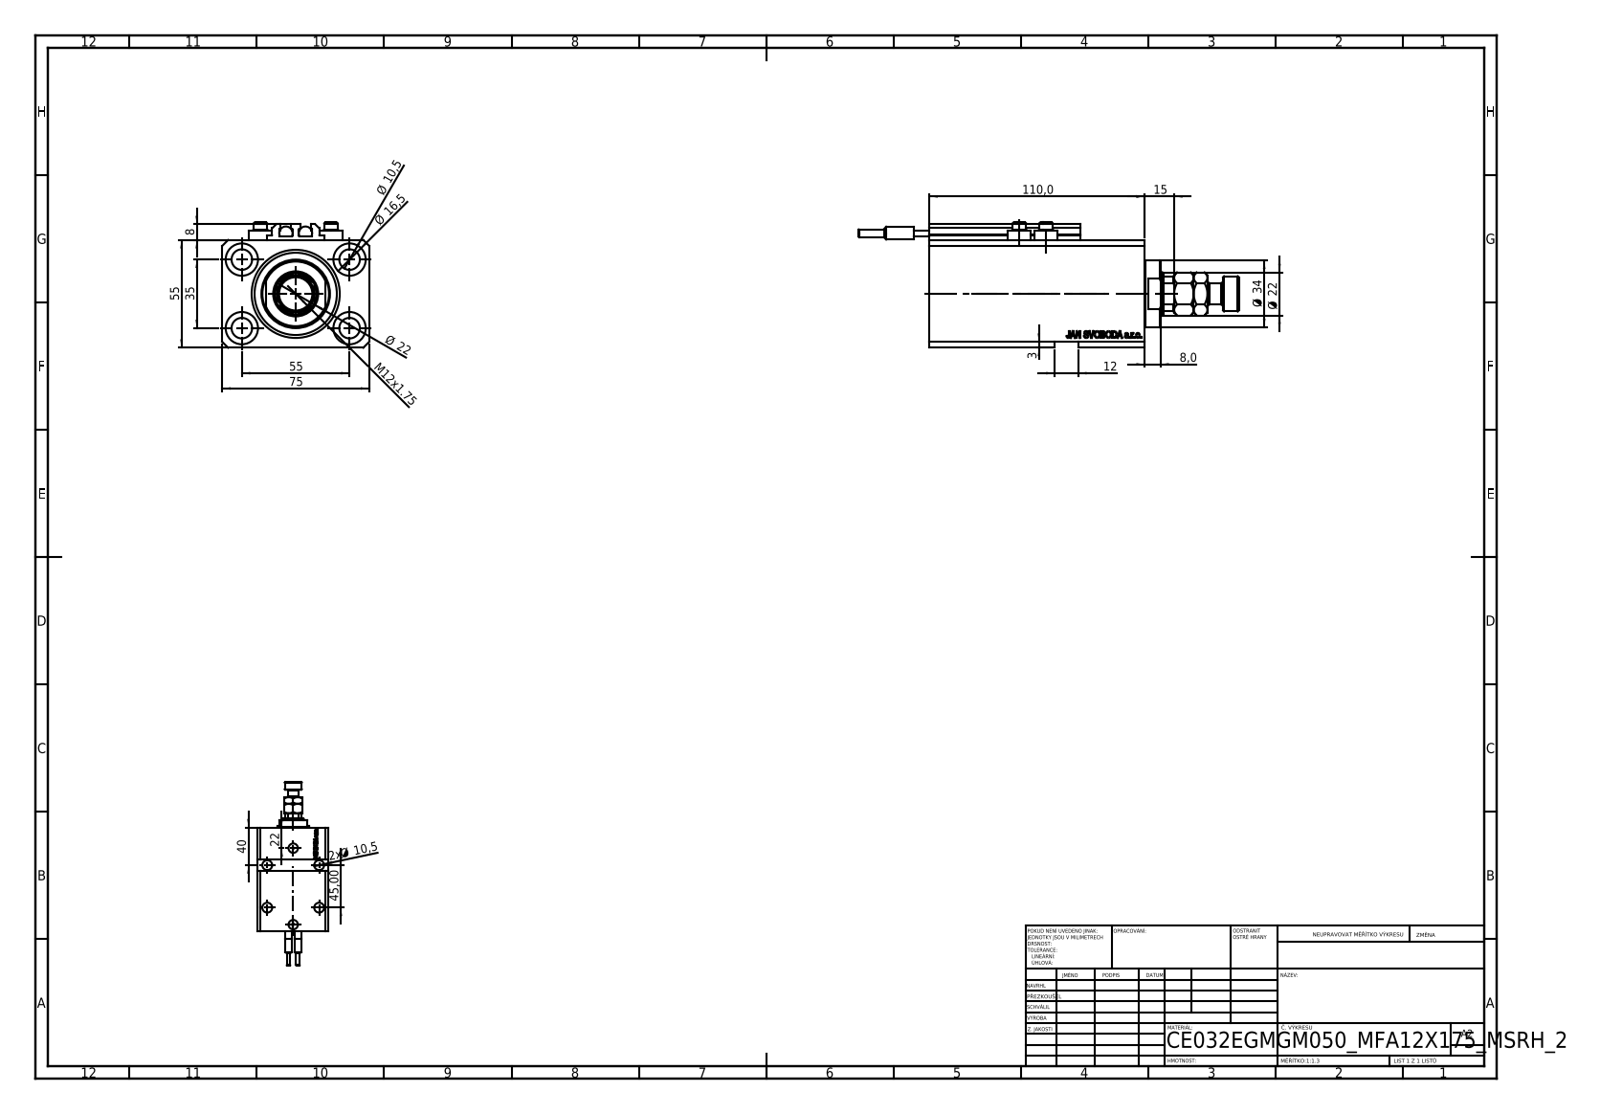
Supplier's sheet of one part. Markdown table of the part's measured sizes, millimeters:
| quantity | value |
| --- | --- |
| part name | V250CE_E_Body; V250CE_VC_E; SWITCH_V250CE; MFA (+2 more) |
| STEP written by | SolidWorks 2019 (CONFIG_CONTROL_DESIGN) |
| units | millimeters |
| bodies | 11 solids, 1188 faces (562 planar, 162 cylindrical, 464 other) |
| overall size | 194 × 75 × 64 |
| volume | 392 978 mm³ |
| surface area | 101 090 mm² |
| round holes (diameter × count) | 10.5 × 9, 1.25 × 4, 4 × 4, 16.5 × 4, 10 × 2, 13.16 × 2, 20 × 2, 22 × 1, 32 × 1, 45 × 1 |
| round bosses / shafts (diameter × count) | 11.6 × 4, 7 × 4, 6.8 × 2, 6.5 × 2, 4 × 2, 34 × 1, 18 × 1, 11 × 1 |
| partial cylindrical surfaces (radius × count) | 0.2 × 10, 10.5 × 1 |
| main face-to-face distances | 55, 75, 15, 3, 110, 57, 95, 9.9, 85.1, 100.1 |
| hole center spacings | 32.6, 32.87, 55, 68.74, 13.6, 14.09, 23.05, 25.81 |
